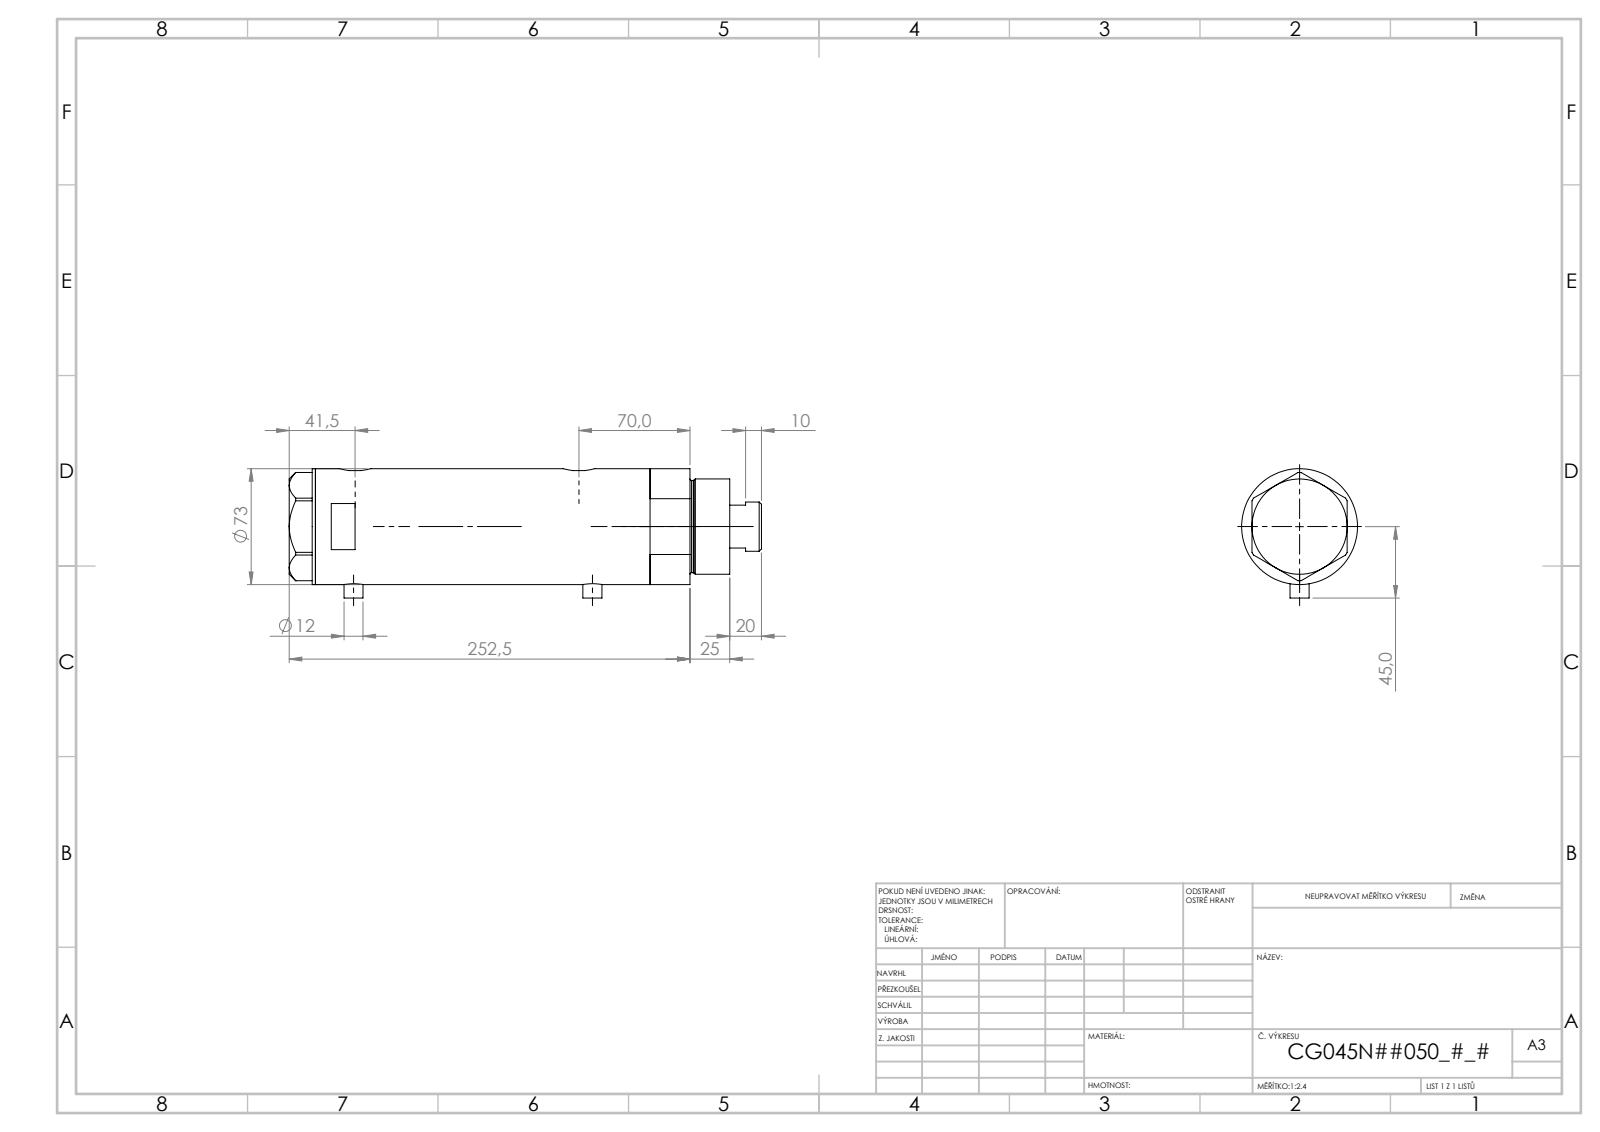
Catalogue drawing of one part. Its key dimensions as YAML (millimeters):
part_name: "V270CG_BACK; V270CG_VC; V270CG_MIDDLE; V270CG_FRONT"
step_written_by: "SolidWorks 2019 (CONFIG_CONTROL_DESIGN)"
units: millimeters
bodies: {solids: 4, faces: 125, planar: 50, cylindrical: 55, other: 20}
overall_size: [241.52, 74.1, 73]
volume: 836716
surface_area: 143502
round_holes:
  - {diameter: 5, count: 2}
  - {diameter: 12.5, count: 2}
  - {diameter: 13.16, count: 2}
  - {diameter: 10.5, count: 1}
  - {diameter: 32, count: 1}
  - {diameter: 33.5, count: 1}
  - {diameter: 45, count: 1}
  - {diameter: 48, count: 1}
  - {diameter: 64, count: 1}
round_bosses_or_shafts:
  - {diameter: 12, count: 2}
  - {diameter: 73, count: 1}
  - {diameter: 60, count: 1}
  - {diameter: 58, count: 1}
  - {diameter: 31, count: 1}
partial_cylinders:
  - {radius: 10, count: 2}
face_to_face_distances: [117.14, 26, 91.14, 16.5, 42.5, 133.64, 205.01, 221.51, 179.01, 87.87]
hole_center_spacings: [101.65, 0.99, 1, 8.5, 8.51, 92.15, 93.14, 93.15]
